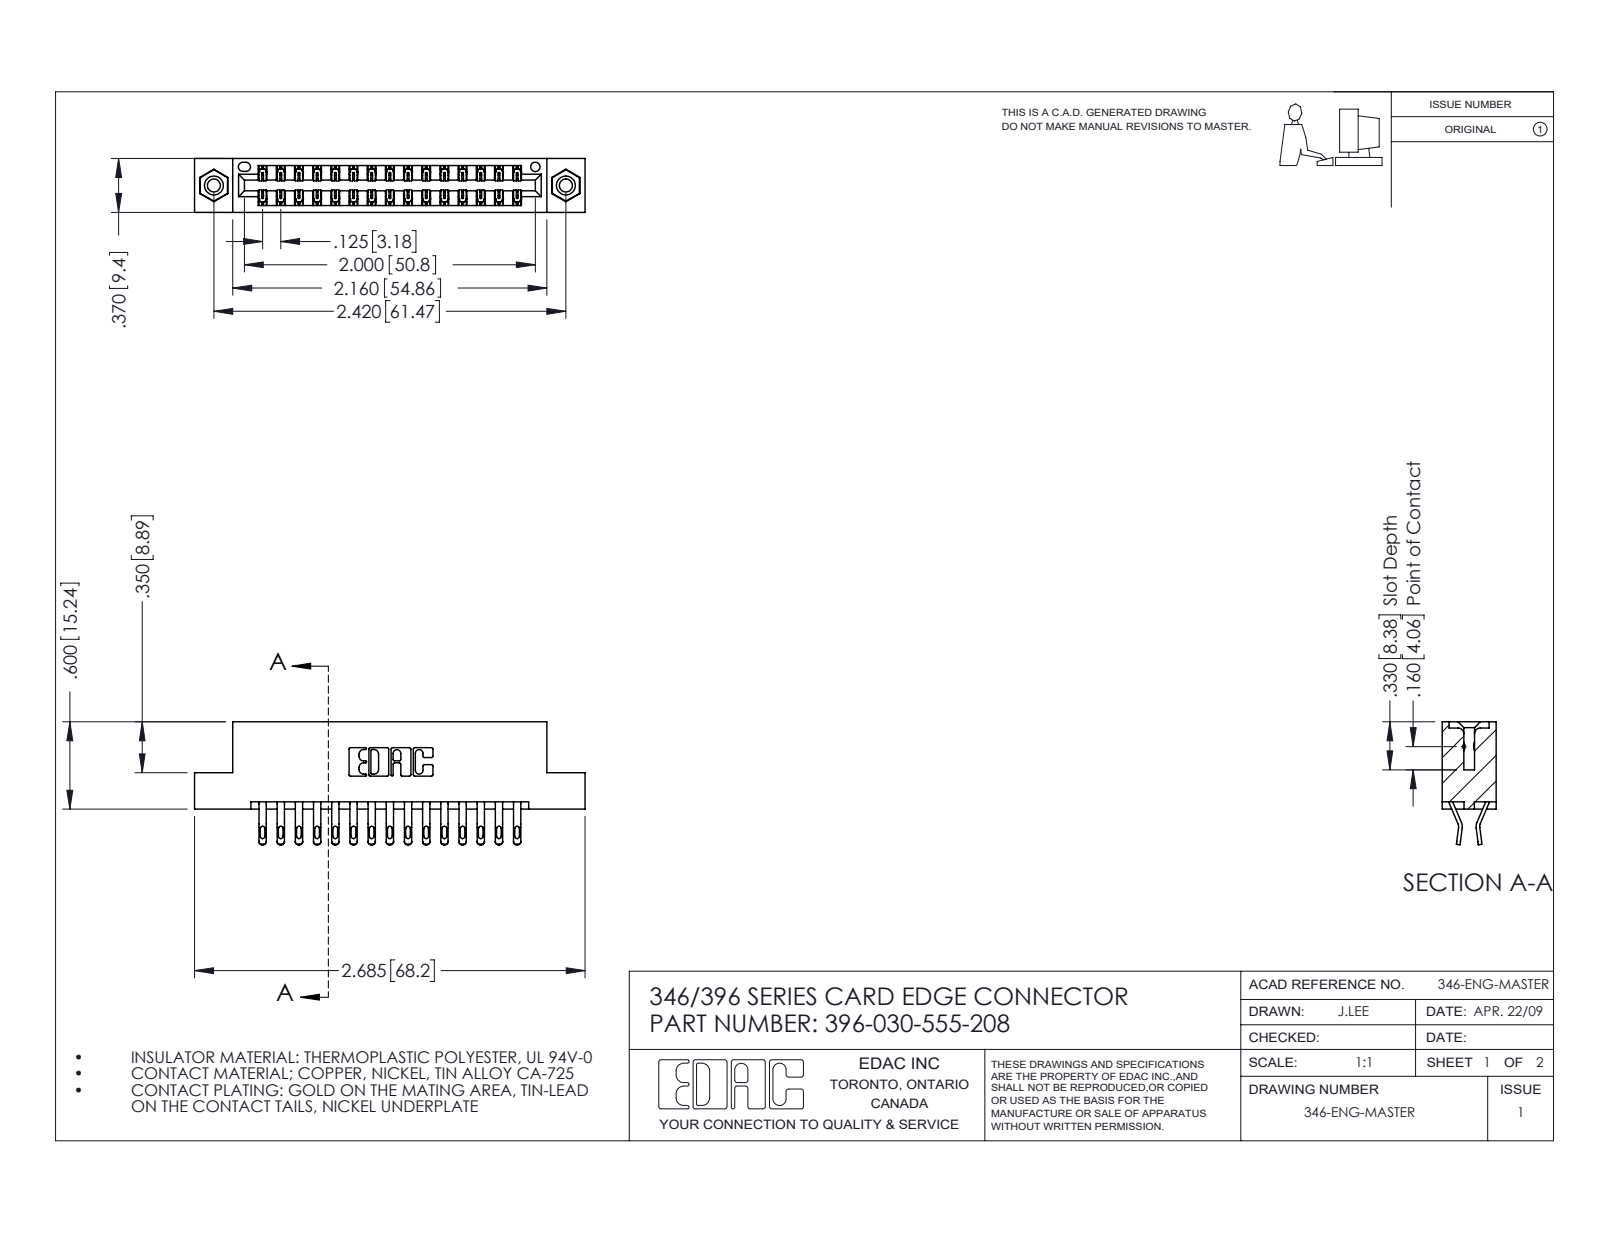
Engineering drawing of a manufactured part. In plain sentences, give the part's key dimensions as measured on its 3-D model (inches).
The part is named "345-292-001_555 Tail; 396-030-555-208; 345-250-001_345-250-003-102; 346 Part_Flush Mounting Lugs - 0.156 Dia-TI". Its 3-D file was written by "SolidWorks 2016 (CONFIG_CONTROL_DESIGN)". It is 33 solids with 1922 faces: 1098 planar, 808 cylindrical and 16 other. Overall it measures 2.685 by 0.845 by 0.37 inches. Its volume is 0.398 cubic inches and its surface area 13.75 square inches. Round holes: 2 of diameter 0.089, 2 of diameter 0.125, 2 of diameter 0.156, 1 of diameter 0.064. Round bosses or shafts: 2 of diameter 0.155. Partial cylindrical surfaces (rounded edges, fillets, slot ends): 60 of radius 0.016, 60 of radius 0.02, 45 of radius 0.006, 22 of radius 0.01, 6 of radius 0.007, 6 of radius 0.031, 3 of radius 0.026, 2 of radius 0.01. The main face-to-face distances are 0.048, 0.322, 0.25, 0.37, 0.025, 0.072, 0.298, 0.275, 0.148, 0.222. The hole center spacings are 0.246, 2.213, 2.42.
